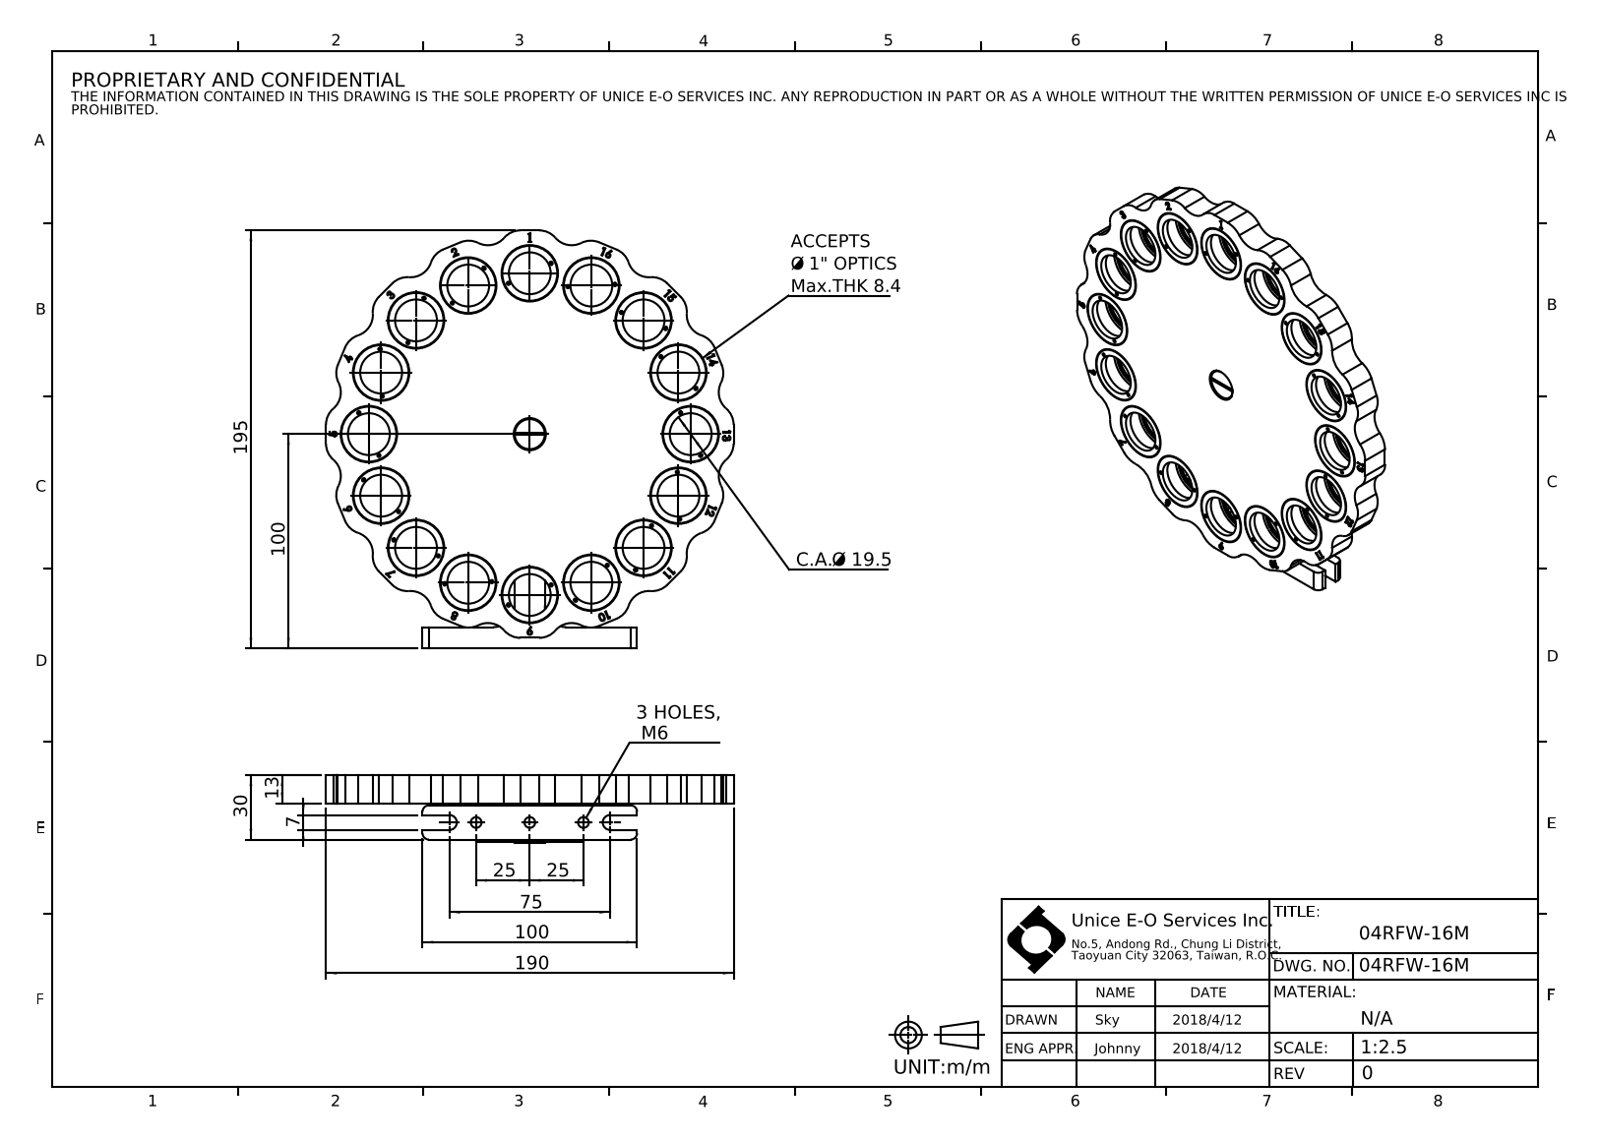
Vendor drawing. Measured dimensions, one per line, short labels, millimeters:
name: 04RFW-16M
written by: SolidWorks 2016 (CONFIG_CONTROL_DESIGN)
unit: mm
bodies: 71 solids, 1325 faces (483 planar, 421 cylindrical, 421 other)
size: 195 × 190 × 31.5
volume: 329 173 mm³; area: 120 170 mm²
holes: 32× ⌀1.5, 16× ⌀19.5, 16× ⌀22, 16× ⌀25.63, 9× ⌀5, 1× ⌀10, 1× ⌀15, 1× ⌀16, 1× ⌀21.5, 1× ⌀34
bosses: 17× ⌀6, 16× ⌀26.3, 16× ⌀25.5, 1× ⌀50, 1× ⌀49.5, 1× ⌀26, 1× ⌀14.5, 1× ⌀14
rounds: 52× R10, 4× R3, 2× R3.5
face distances: 13, 1, 17, 16, 14, 18, 2, 10, 3, 12
hole spacings: 29.26, 57.4, 75, 124.72, 138.58, 21, 106.06, 83.33
